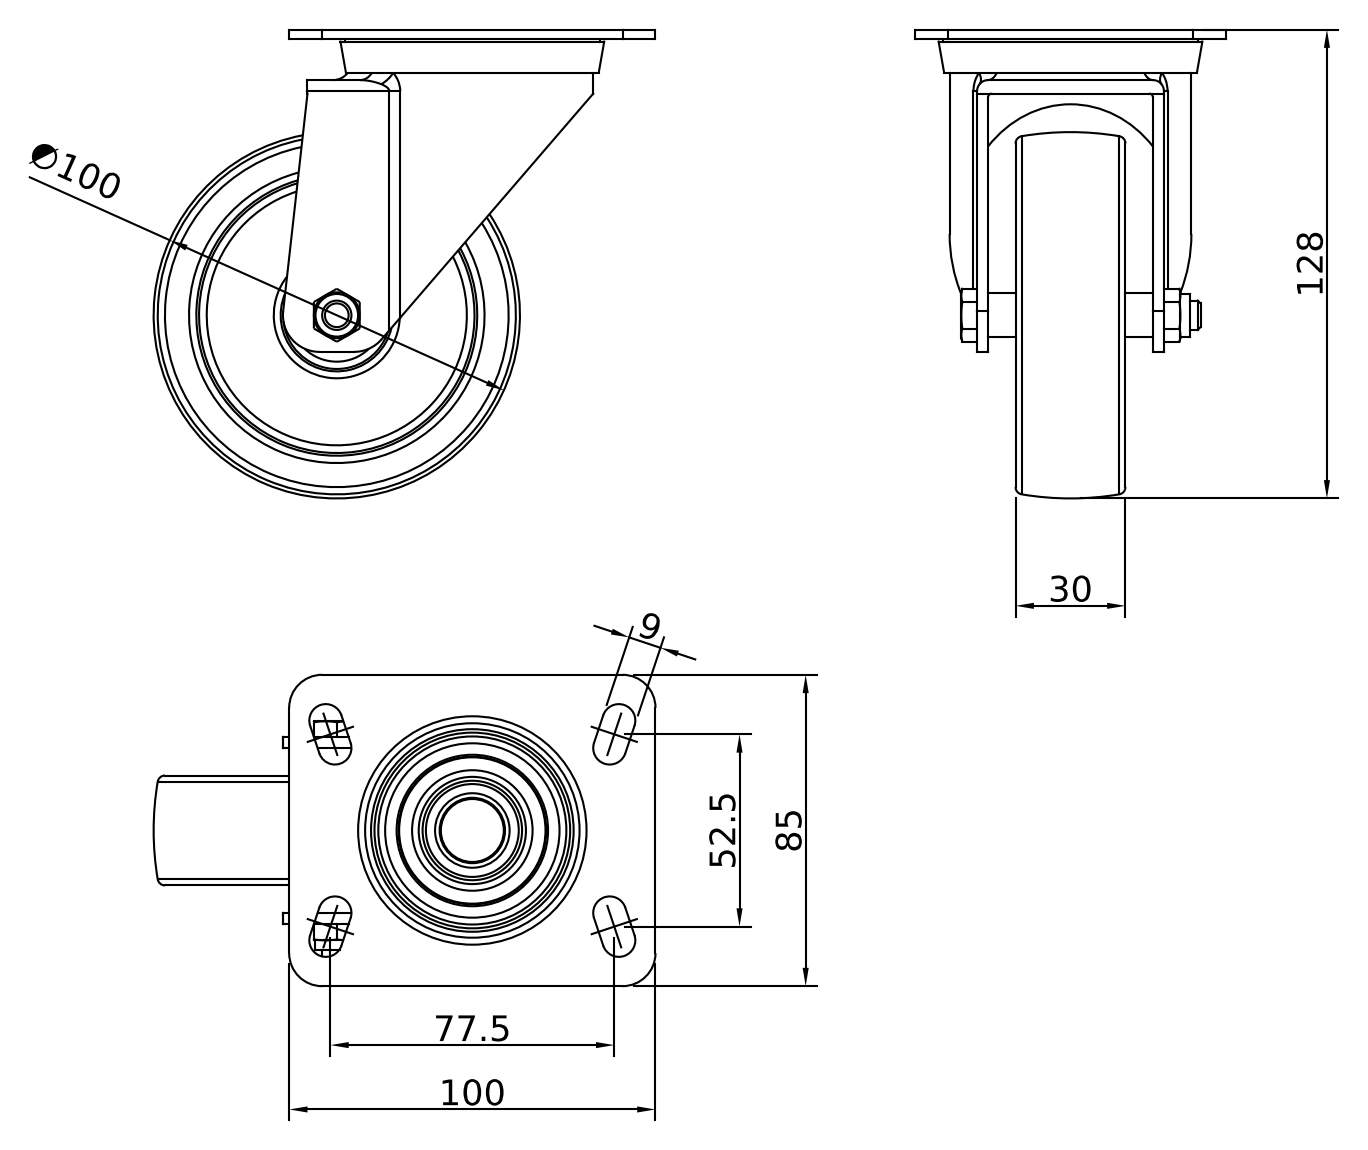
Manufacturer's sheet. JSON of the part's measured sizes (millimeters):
{"part_name": "CRUST0000155", "step_written_by": "Autodesk Inventor 2022 (AUTOMOTIVE_DESIGN)", "units": "millimeters", "bodies": {"solids": 1, "faces": 139, "planar": 57, "cylindrical": 34, "other": 48}, "overall_size": [137, 128, 85], "volume_mm3": 220892, "surface_area_mm2": 71349, "round_holes": [[9, 1], [40.35, 1], [61, 1]], "round_bosses_or_shafts": [[69.6, 1], [12, 1], [11.63, 1], [8, 1]], "partial_cylinders_radius": [[4.5, 8], [9, 4], [1, 2], [3, 2], [5, 2], [10, 2], [33, 1]], "face_to_face_distances": [2.5, 10.5, 7.5, 37.5, 3, 40.5, 48, 11.5, 14, 30]}
